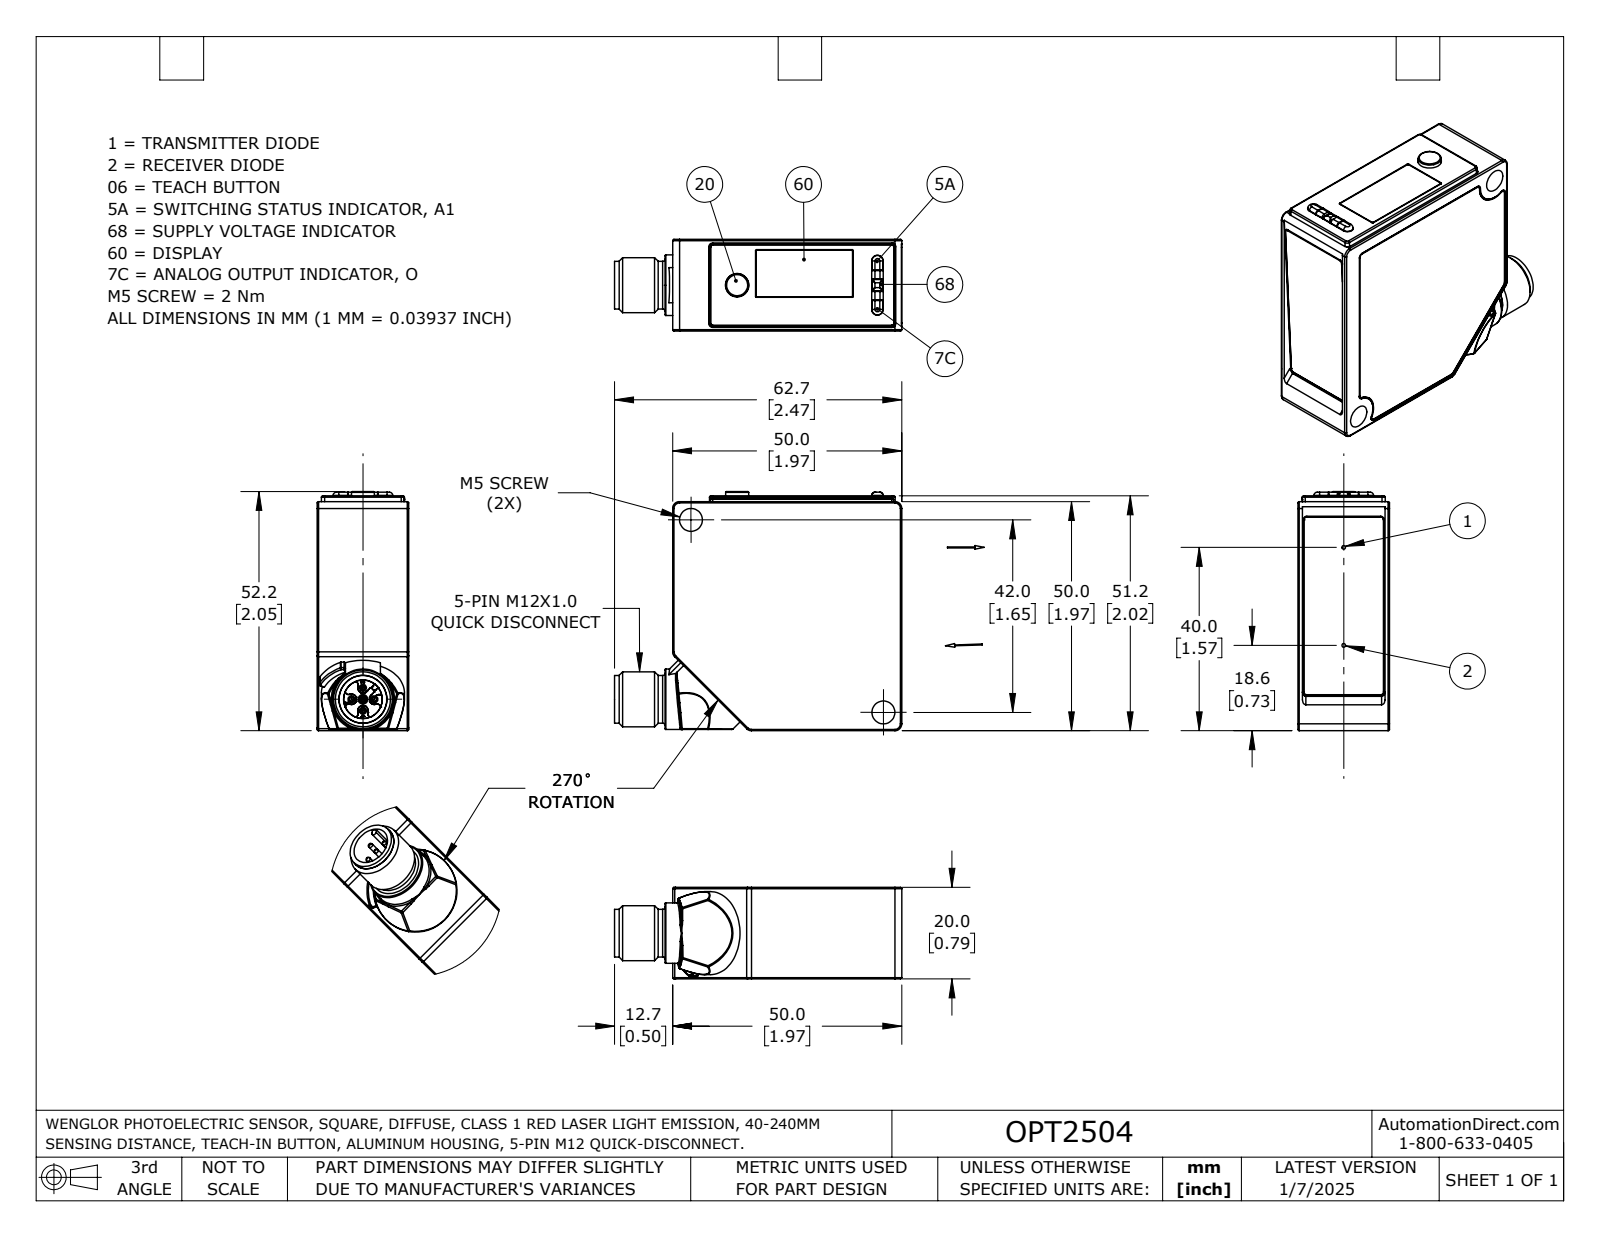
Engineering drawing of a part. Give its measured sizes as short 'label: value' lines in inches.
name: OPT2501_OPT2504_OPT2507_OPT2510
written by: SolidWorks 2024 (AUTOMOTIVE_DESIGN)
unit: in
bodies: 3 solids, 426 faces (182 planar, 131 cylindrical, 113 other)
size: 3.176 × 2.055 × 0.787
volume: 3.065 in³; area: 15.96 in²
holes: 5× ⌀0.06, 1× ⌀0.201
bosses: 5× ⌀0.039, 2× ⌀0.008, 1× ⌀0.713, 1× ⌀0.52, 1× ⌀0.472, 1× ⌀0.409, 1× ⌀0.197, 1× ⌀0.083
rounds: 35× R0.012, 11× R0.026, 8× R0.008, 7× R0.031, 6× R0.027, 6× R0.028, 6× R0.03, 5× R0.059
face distances: 0.785, 2.017, 0.787, 1.969, 0.049, 0.037, 1.958, 2.007, 0.748, 0.039
hole spacings: 0.098, 0.139, 0.197
